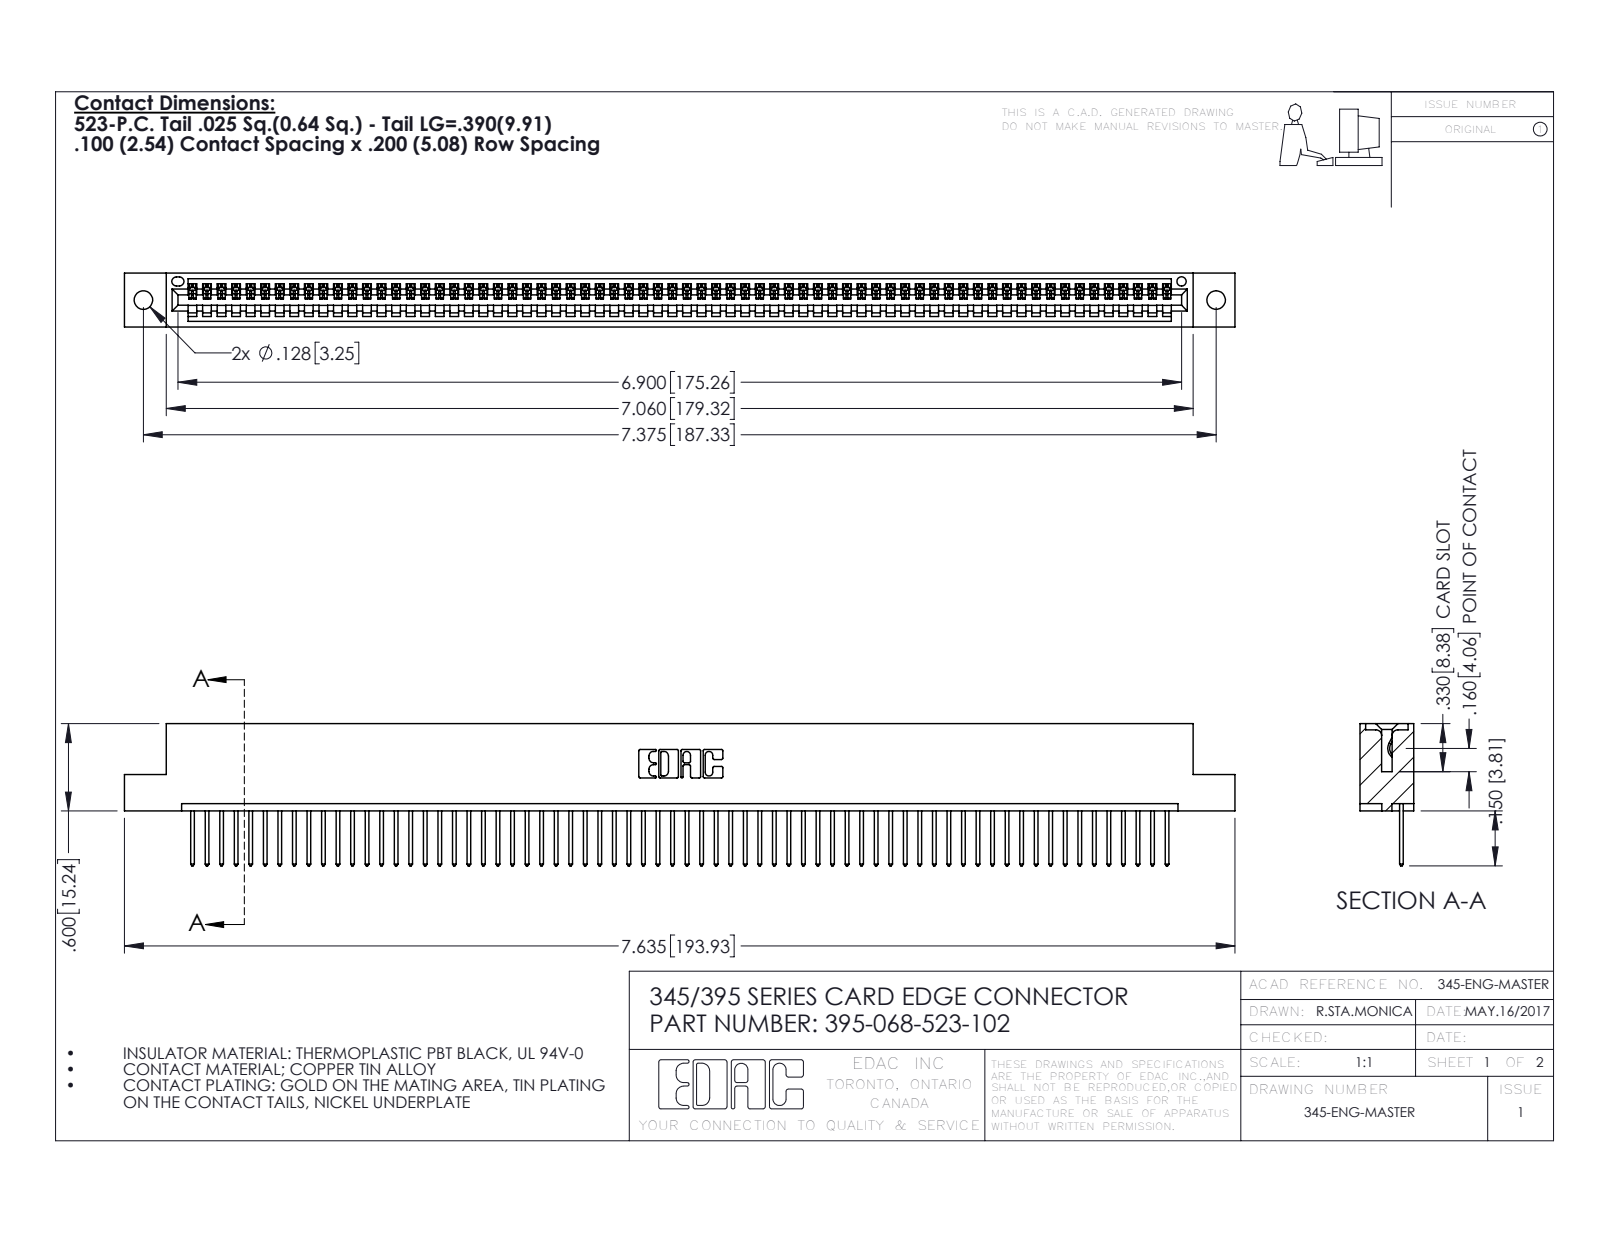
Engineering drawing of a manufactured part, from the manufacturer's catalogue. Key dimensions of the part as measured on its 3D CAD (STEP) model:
Part name (STEP PRODUCT): 395-068-523-102; 345-292-001_345-293-123; 345 Part_Flush Mounting Lugs - 0.128 Dia
STEP written by: SolidWorks 2016 (CONFIG_CONTROL_DESIGN)
Units: inches
Bodies: 69 solids, 4070 faces (2800 planar, 1270 cylindrical, 0 other)
Overall size (bounding box): 7.635 × 0.977 × 0.37
Volume: 1.133 in³ · Surface area: 38.49 in²
Round holes (diameter × count): ⌀0.128 ×2, ⌀0.064 ×1
Partial cylindrical surfaces — rounded edges, fillets, slot ends (radius × count): R0.006 ×136, R0.01 ×136, R0.01 ×22, R0.007 ×6, R0.031 ×6, R0.026 ×3, R0.031 ×2, R0.04 ×2
Main face-to-face distances: 0.298, 0.072, 0.37, 0.2, 0.098, 0.272, 0.025, 0.225, 0.149, 0.072
Hole centre spacings: 0.27, 7.139, 7.375
